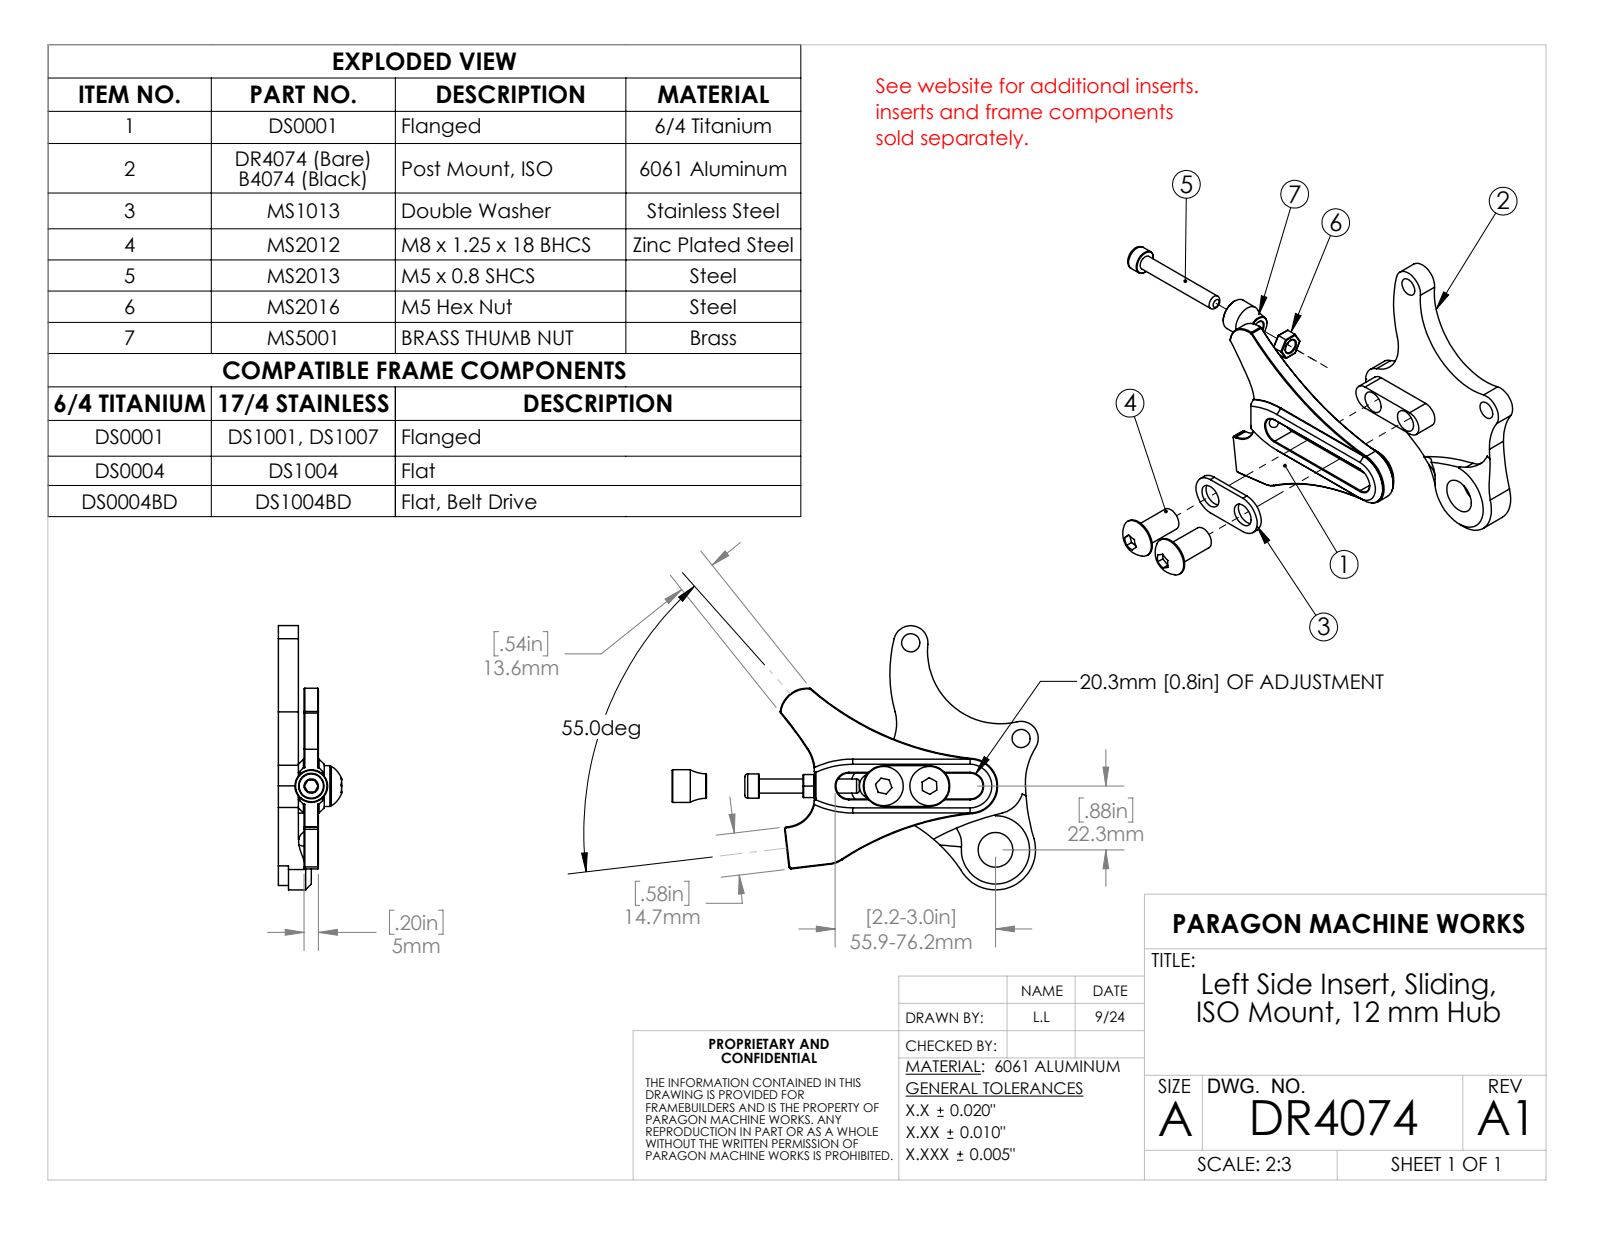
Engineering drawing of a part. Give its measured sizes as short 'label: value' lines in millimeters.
name: DR4074
written by: SolidWorks 2023 (AUTOMOTIVE_DESIGN)
unit: mm
bodies: 1 solid, 45 faces (11 planar, 30 cylindrical, 4 other)
size: 92.3 × 65.6 × 14.9
volume: 21 960 mm³; area: 9 748 mm²
holes: 2× ⌀6.4, 2× ⌀7.9, 1× ⌀12.1
rounds: 2× R4.5, 2× R6, 2× R50.8, 1× R7.6, 1× R7.6, 1× R9.8, 1× R10, 1× R14
face distances: 7, 11.5, 4.5, 3.5, 3.5, 8, 9, 14.9, 11.4, 8
hole spacings: 16, 32.1, 36, 39.9, 45, 50.4, 50.8, 50.9
